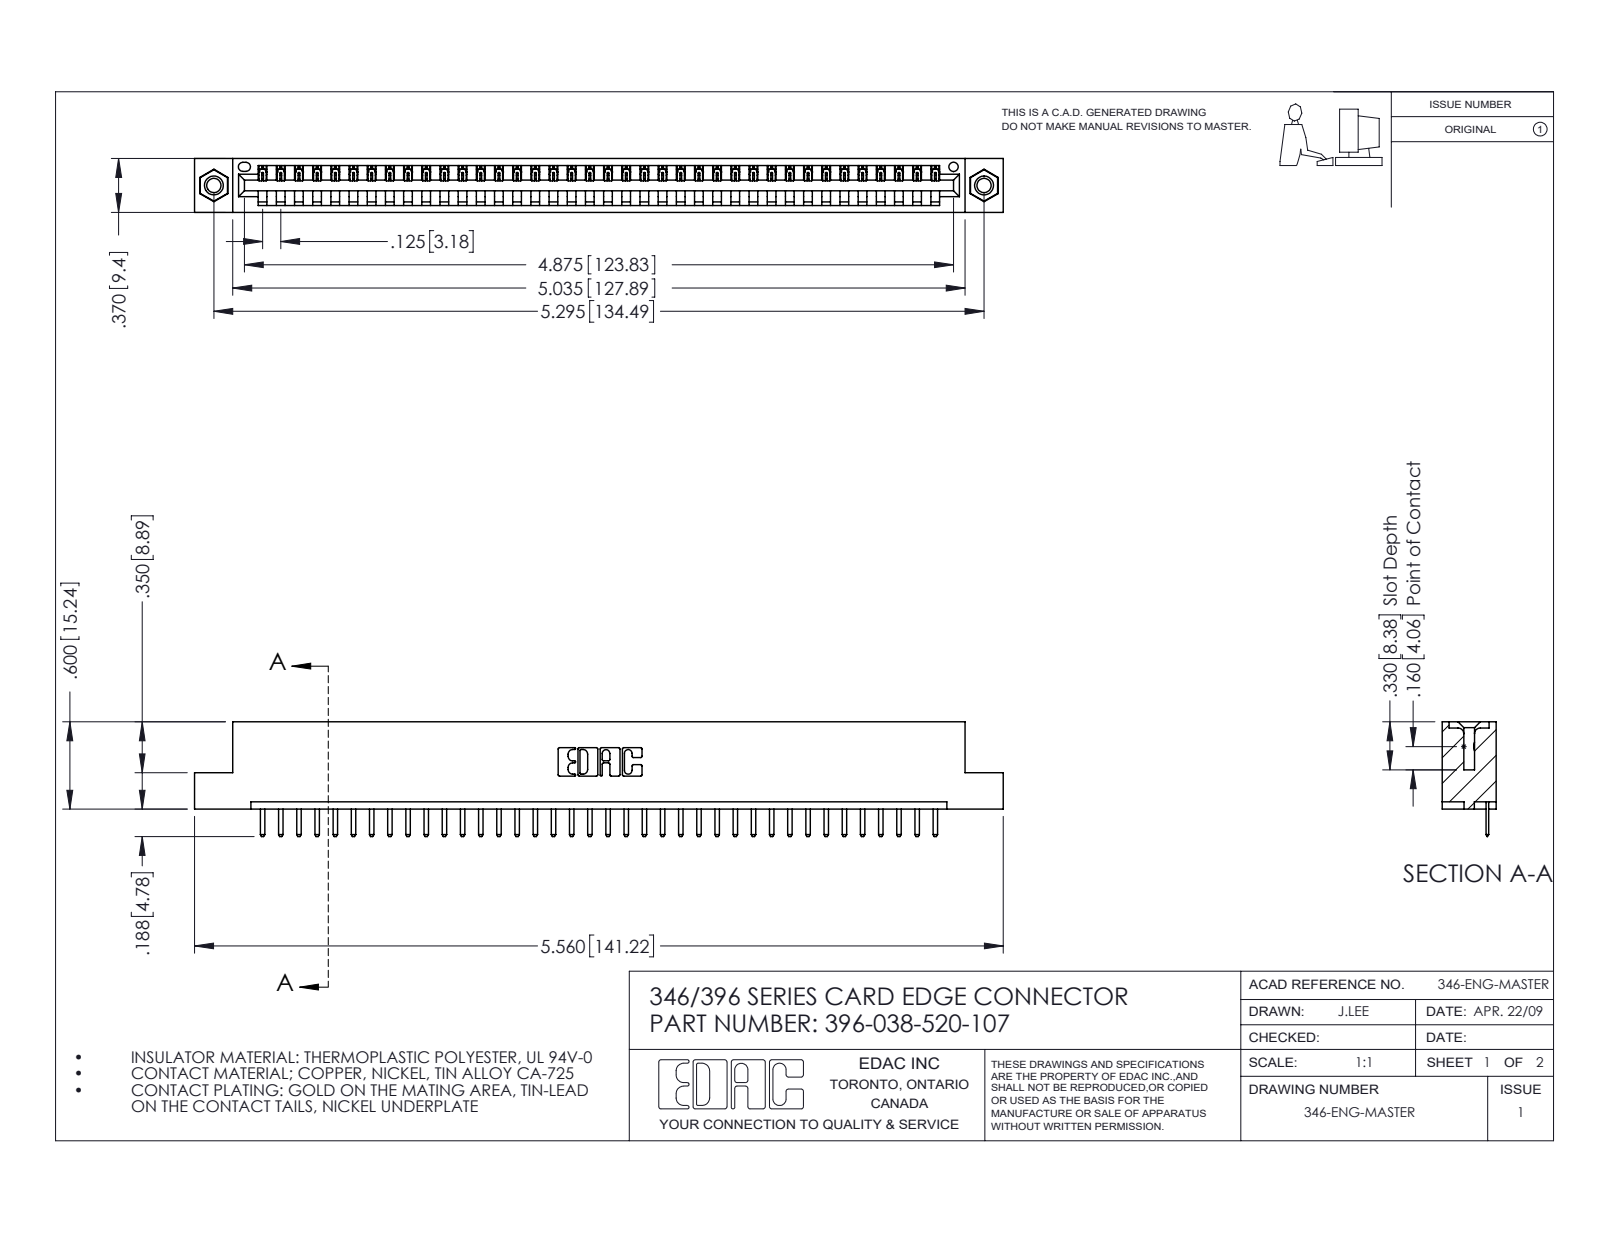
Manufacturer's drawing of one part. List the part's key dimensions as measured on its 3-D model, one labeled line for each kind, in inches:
Part name (STEP PRODUCT): 345-250-001_345-250-005-103; 396-038-520-107; 345-292-001_345-293-120; 346 Part_Flush Mounting Lugs - 0.156 Dia-TI
STEP written by: SolidWorks 2016 (CONFIG_CONTROL_DESIGN)
Units: inches
Bodies: 41 solids, 2538 faces (1704 planar, 818 cylindrical, 16 other)
Overall size (bounding box): 5.56 × 0.788 × 0.37
Volume: 0.816 in³ · Surface area: 25.32 in²
Round holes (diameter × count): ⌀0.098 ×2, ⌀0.125 ×2, ⌀0.156 ×2, ⌀0.064 ×1
Round bosses / shafts (diameter × count): ⌀0.155 ×2
Partial cylindrical surfaces — rounded edges, fillets, slot ends (radius × count): R0.01 ×78, R0.006 ×76, R0.01 ×22, R0.007 ×6, R0.031 ×6, R0.026 ×3, R0.031 ×2, R0.04 ×2
Main face-to-face distances: 0.048, 0.322, 0.37, 0.25, 0.148, 0.222, 0.1, 0.174, 0.072, 0.298
Hole centre spacings: 0.246, 5.086, 5.295
